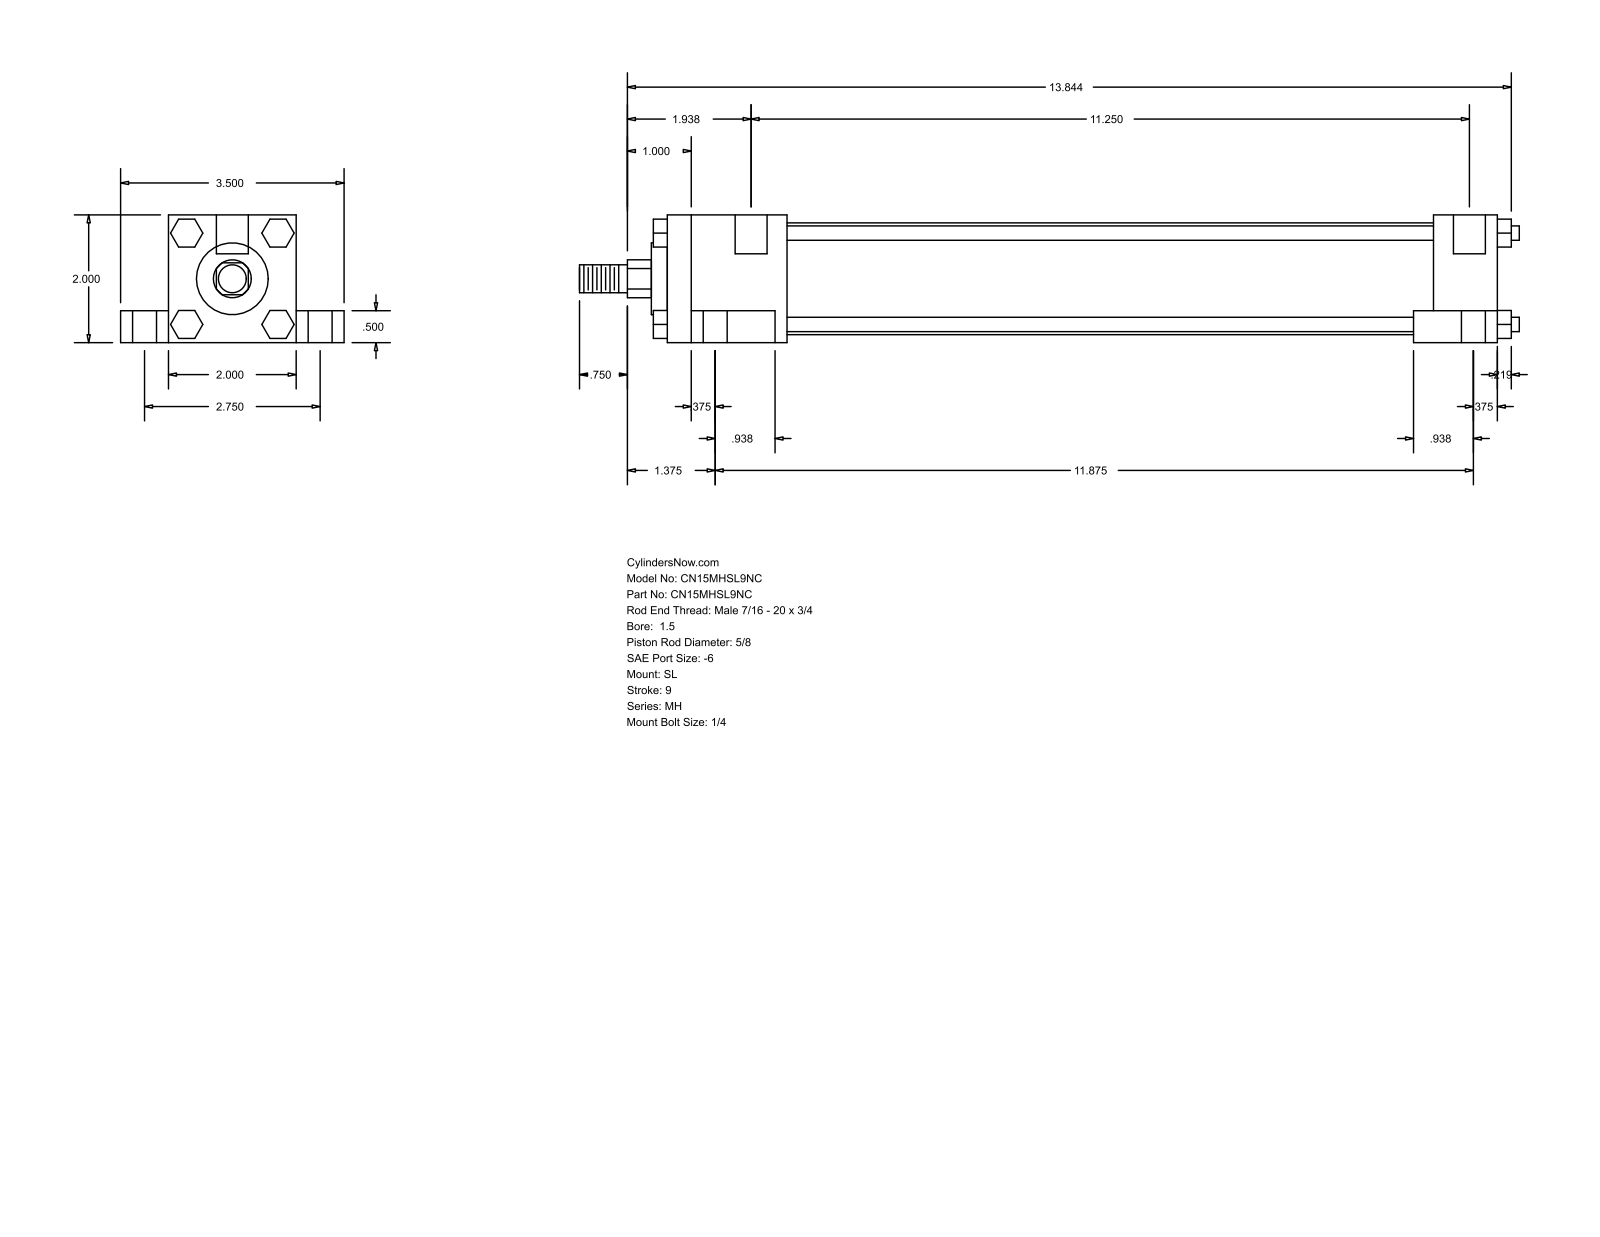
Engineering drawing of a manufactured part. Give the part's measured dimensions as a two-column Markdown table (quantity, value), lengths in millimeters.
| quantity | value |
| --- | --- |
| part name | MH_SL__0150_0.625 |
| STEP written by | GSSL Pune (CONFIG_CONTROL_DESIGN) |
| units | millimeters |
| bodies | 0 solids, 148 faces (112 planar, 36 cylindrical, 0 other) |
| overall size | 373.86 × 88.9 × 50.8 |
| round holes (diameter × count) | 5.56 × 4, 9.53 × 4, 15.88 × 4, 12.7 × 2 |
| round bosses / shafts (diameter × count) | 5.71 × 4, 44.45 × 1, 28.57 × 1, 15.88 × 1, 11.11 × 1 |
| partial cylindrical surfaces (radius × count) | 7.54 × 1 |
| main face-to-face distances | 50.8, 38.1, 19.05, 12.7, 69.85, 330.19, 9.52, 304.8, 25.39, 47.62 |
| hole center spacings | 34.96, 36.65, 37.73, 69.84, 288.92, 289.45, 292.6, 301.63 |
